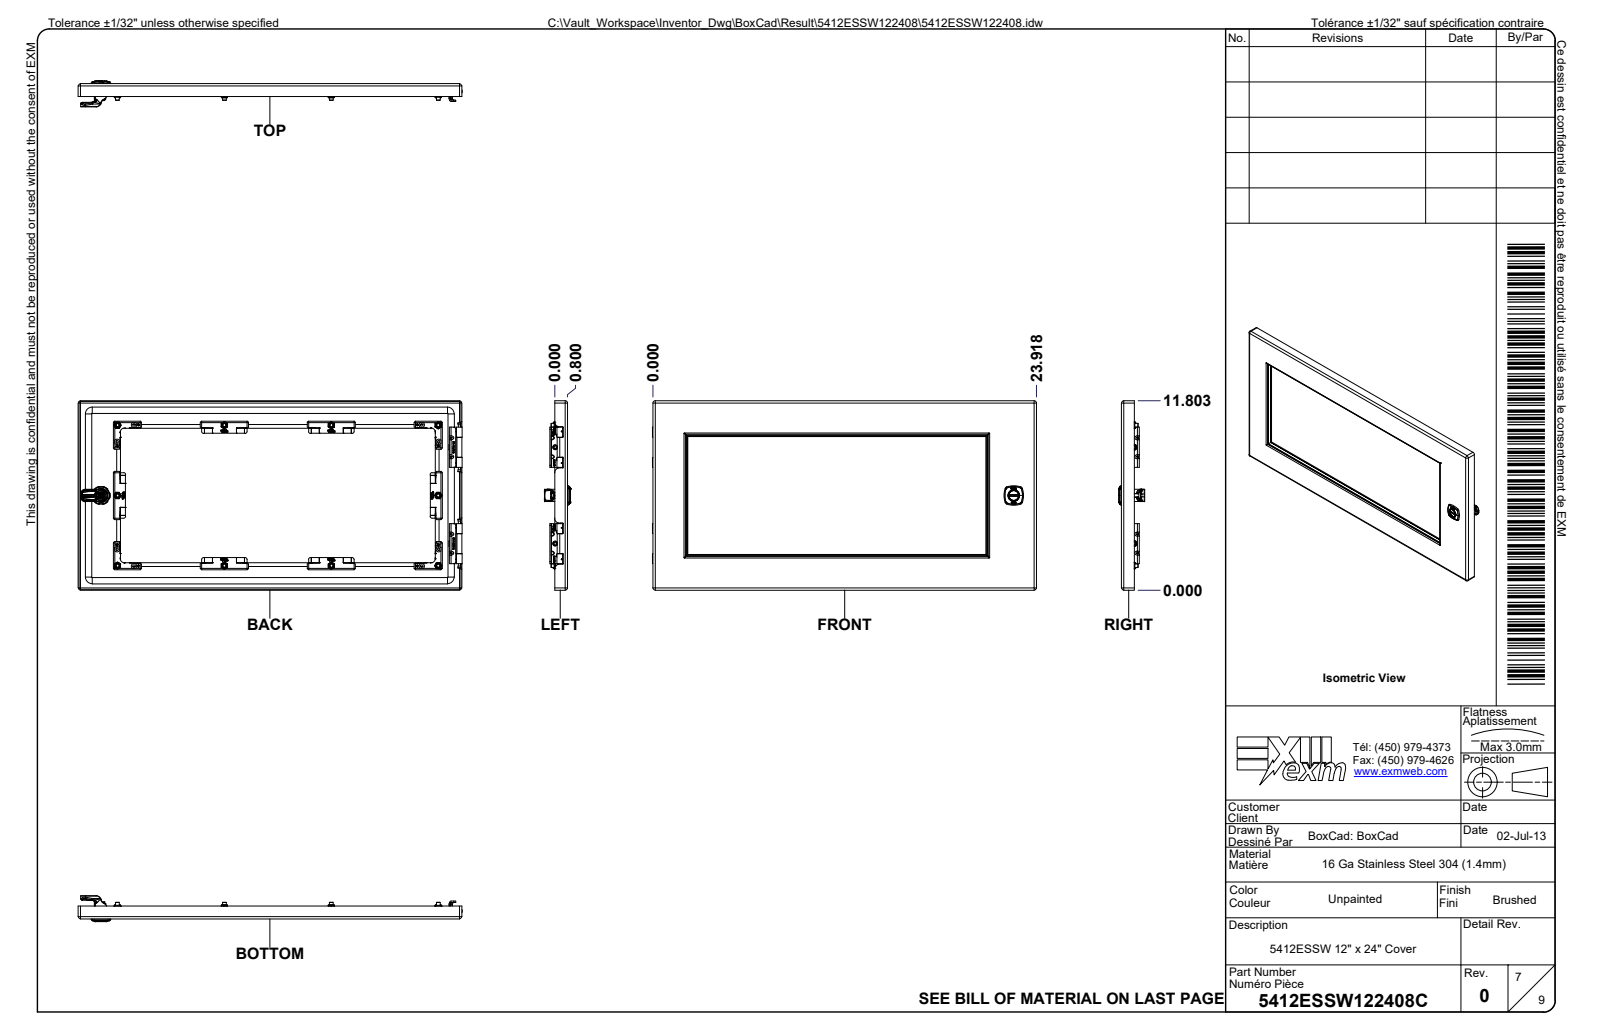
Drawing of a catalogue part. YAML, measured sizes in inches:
part_name: "5412ESSW122408; 5412ESSW122408B; 5412ESSW122408B-P; STK-Q-16020 (+8 more)"
step_written_by: "Autodesk Inventor 2024 (AUTOMOTIVE_DESIGN)"
units: inches
bodies: {solids: 85, faces: 12270, planar: 5522, cylindrical: 2482, other: 4266}
overall_size: [24, 12, 9.306]
volume: 153.8
surface_area: 3673
round_holes:
  - {diameter: 0.29, count: 16}
  - {diameter: 0.03, count: 15}
  - {diameter: 0.315, count: 14}
  - {diameter: 0.201, count: 13}
  - {diameter: 0.197, count: 10}
  - {diameter: 0.276, count: 10}
  - {diameter: 0.374, count: 10}
  - {diameter: 0.173, count: 8}
  - {diameter: 0.044, count: 4}
  - {diameter: 0.27, count: 4}
  - {diameter: 0.39, count: 4}
  - {diameter: 0.236, count: 2}
round_bosses_or_shafts:
  - {diameter: 0.03, count: 15}
  - {diameter: 0.232, count: 14}
  - {diameter: 0.354, count: 10}
  - {diameter: 0.271, count: 8}
  - {diameter: 0.039, count: 8}
  - {diameter: 0.717, count: 4}
  - {diameter: 0.311, count: 4}
  - {diameter: 0.262, count: 4}
partial_cylinders:
  - {radius: 0.02, count: 156}
  - {radius: 0.031, count: 108}
  - {radius: 0.039, count: 90}
  - {radius: 0.086, count: 62}
  - {radius: 0.008, count: 54}
  - {radius: 0.035, count: 30}
  - {radius: 0.084, count: 28}
  - {radius: 0.008, count: 20}
face_to_face_distances: [0.053, 11.947, 9.082, 0.927, 0.874, 0.105, 1.032, 0.979, 11.894, 12]
hole_center_spacings: [1.028, 10.999, 1.026, 1.492, 1.591, 3.347, 4.374, 4.52]
